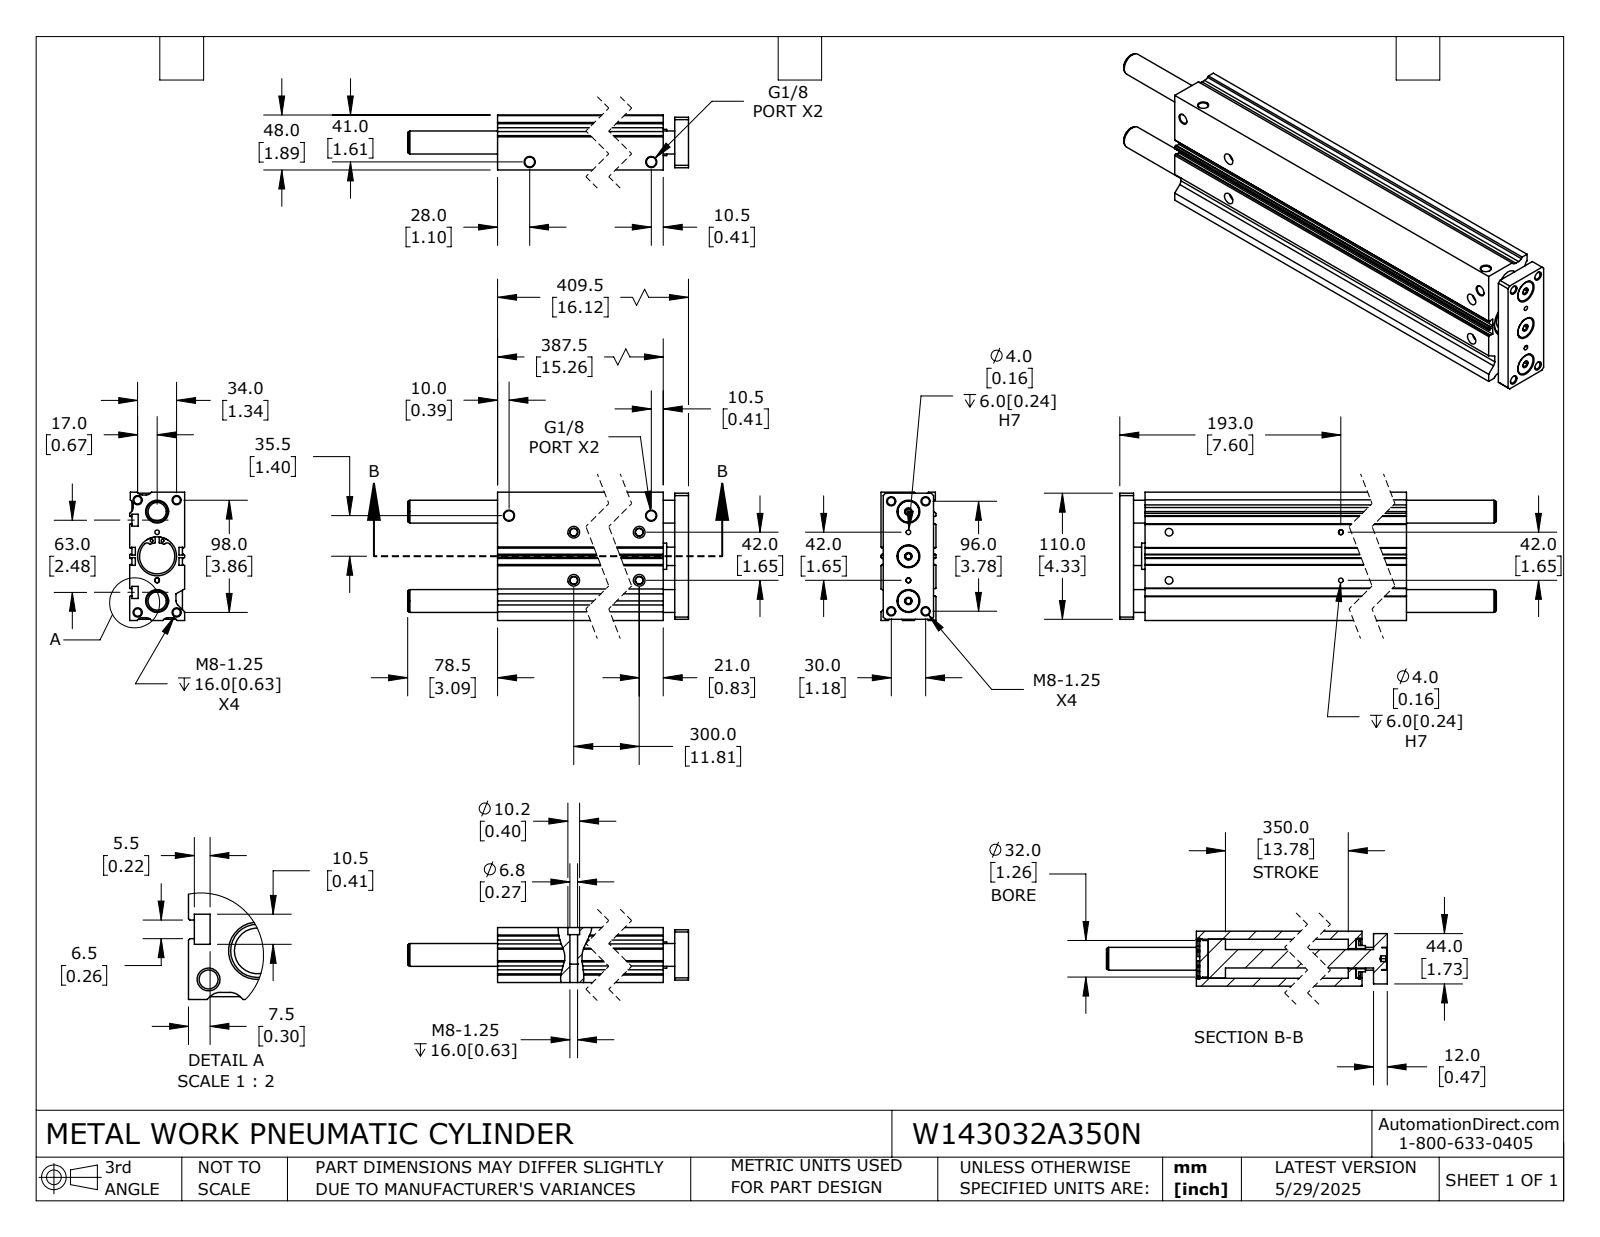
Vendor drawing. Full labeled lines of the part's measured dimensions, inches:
Part name (STEP PRODUCT): W143032A350N_BODY; W143032A350N_ROD; W143032A350N
STEP written by: SolidWorks 2024 (CONFIG_CONTROL_DESIGN)
Units: inches
Bodies: 6 solids, 394 faces (195 planar, 149 cylindrical, 50 other)
Overall size (bounding box): 19.213 × 4.409 × 1.89
Volume: 106.6 in³ · Surface area: 579.3 in²
Round holes (diameter × count): ⌀0.262 ×10, ⌀0.098 ×4, ⌀0.157 ×4, ⌀0.268 ×4, ⌀0.337 ×4, ⌀0.402 ×4, ⌀0.197 ×3, ⌀0.787 ×3, ⌀0.262 ×2, ⌀0.697 ×1, ⌀1.211 ×1
Round bosses / shafts (diameter × count): ⌀0.748 ×3, ⌀1.406 ×2, ⌀1.339 ×1, ⌀1.26 ×1, ⌀0.906 ×1, ⌀0.63 ×1
Partial cylindrical surfaces — rounded edges, fillets, slot ends (radius × count): R0.197 ×9, R0.079 ×4, R0.118 ×4, R0.507 ×2
Main face-to-face distances: 1.89, 0.098, 0.295, 1.693, 0.197, 1.594, 4.409, 0.079, 0.118, 1.398
Hole centre spacings: 0.088, 0.348, 0.566, 0.689, 0.776, 1.019, 1.216, 1.261
